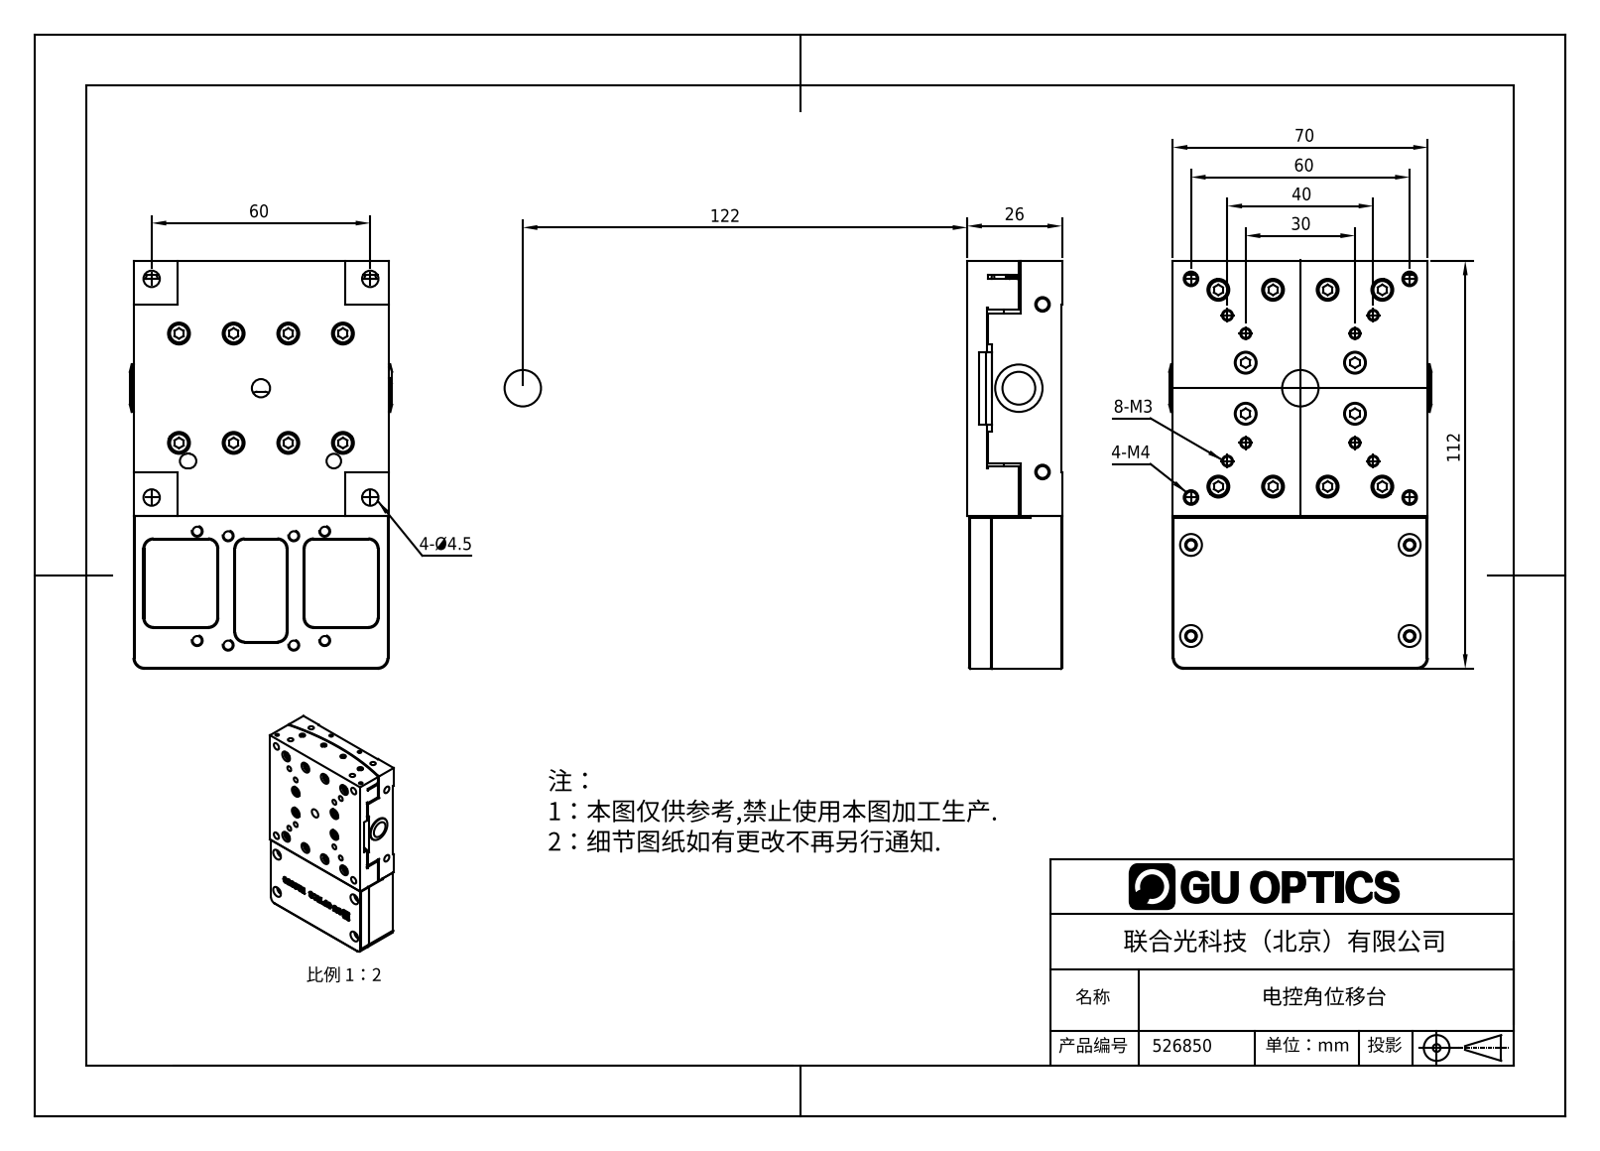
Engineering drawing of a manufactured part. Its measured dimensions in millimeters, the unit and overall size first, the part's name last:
Units: millimetres
Overall size (bounding box): 153 × 112 × 72
Round holes (diameter × count): ⌀3 ×35, ⌀6 ×26, ⌀3.5 ×20, ⌀2.5 ×17, ⌀2.46 ×12, ⌀4 ×10, ⌀2 ×9, ⌀3.24 ×8, ⌀3.2 ×6, ⌀1.6 ×5, ⌀4.5 ×4, ⌀7.5 ×4
Round bosses / shafts (diameter × count): ⌀5.5 ×20, ⌀3 ×16, ⌀13 ×1
Partial cylindrical surfaces — rounded edges, fillets, slot ends (radius × count): R3 ×13, R2.5 ×12, R2 ×10, R0.79 ×2, R1.23 ×2, R1.5 ×2, R1.62 ×1, R2.25 ×1
Main face-to-face distances: 10.5, 1.5, 0.5, 70, 25.7, 4.5, 13.5, 5, 42, 21
Hole centre spacings: 30, 42.43, 10.97, 16.77, 23.24, 27.04, 27.46, 50.99
Bodies: 0 solids, 1740 faces (639 planar, 598 cylindrical, 503 other)
Part name (STEP PRODUCT): 电控角位移台
STEP written by: SolidWorks 2016 (AUTOMOTIVE_DESIGN)
